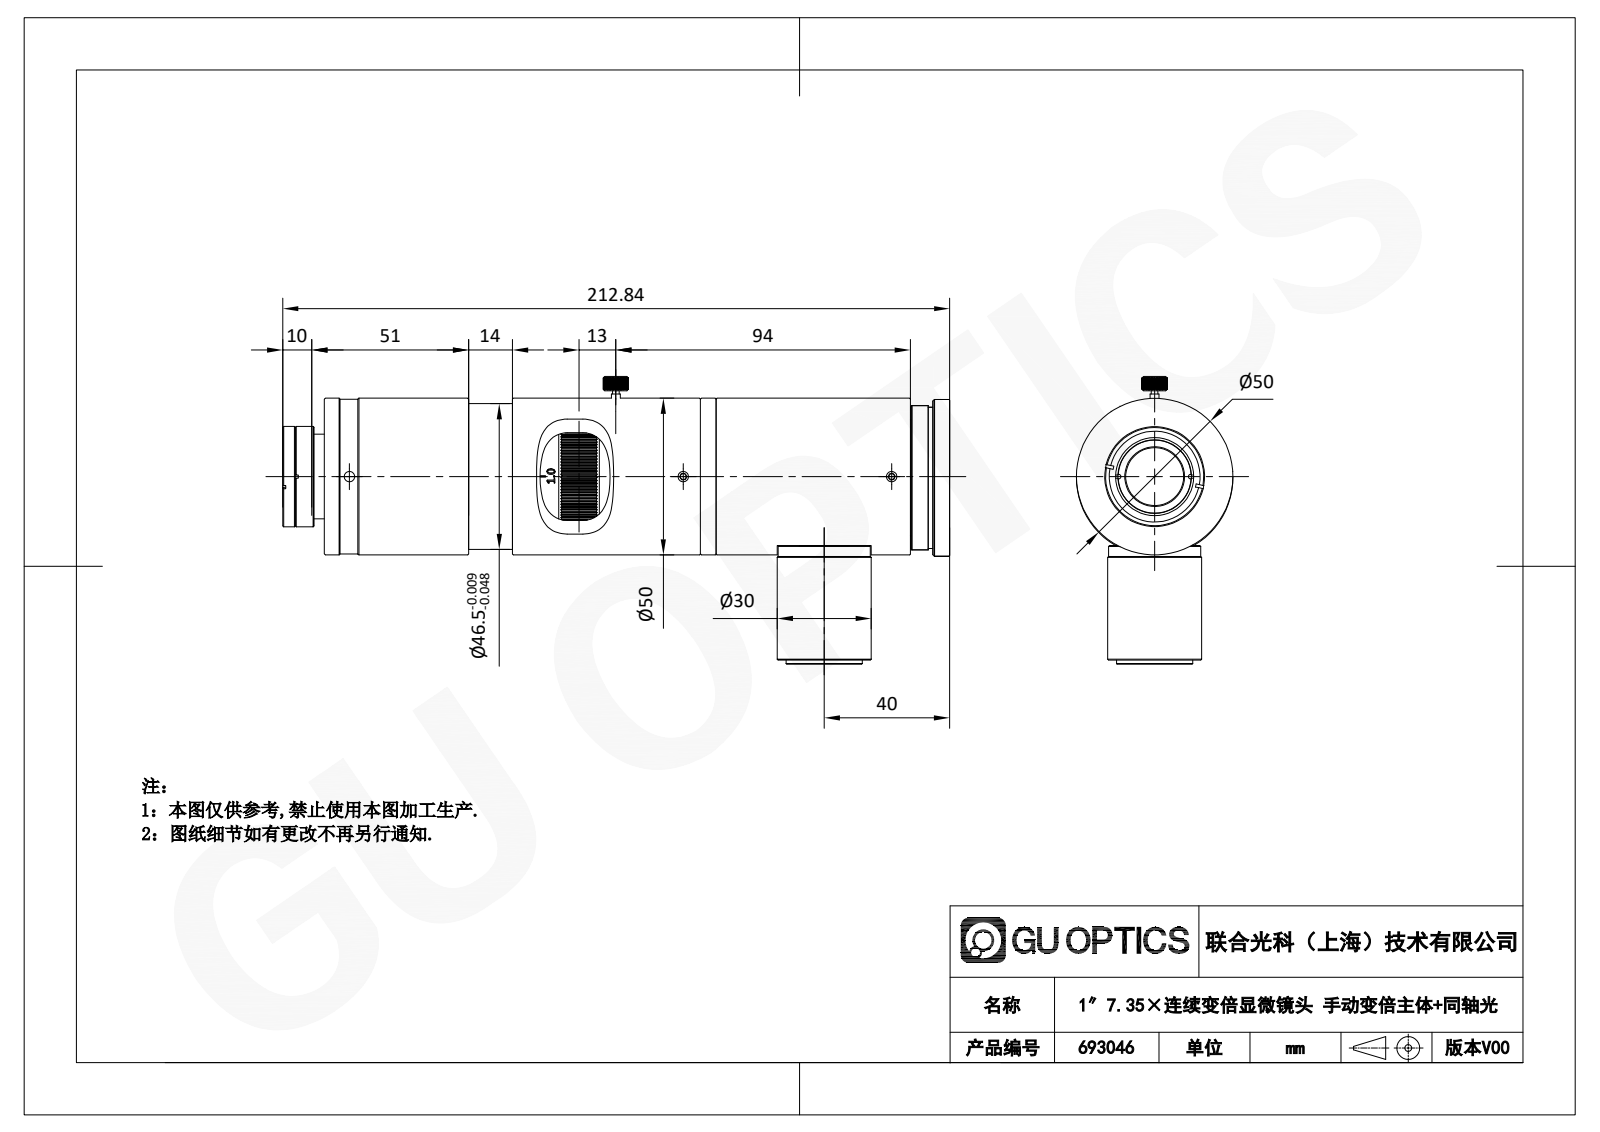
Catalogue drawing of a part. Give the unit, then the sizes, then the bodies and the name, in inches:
Units: inches
Overall size (bounding box): 8.38 × 3.612 × 1.969
Round holes (diameter × count): ⌀0.13 ×9, ⌀0.079 ×6, ⌀0.063 ×3, ⌀0.081 ×2, ⌀0.094 ×2, ⌀0.807 ×2, ⌀1.417 ×2, ⌀0.069 ×1, ⌀0.089 ×1, ⌀0.177 ×1, ⌀0.591 ×1, ⌀0.605 ×1
Round bosses / shafts (diameter × count): ⌀0.157 ×7, ⌀1.969 ×2, ⌀1.945 ×1, ⌀1.831 ×1, ⌀1.811 ×1, ⌀1.776 ×1, ⌀1.693 ×1, ⌀1.654 ×1
Partial cylindrical surfaces — rounded edges, fillets, slot ends (radius × count): R0.024 ×9, R0.03 ×6, R0.394 ×4, R0.157 ×1, R0.396 ×1, R0.807 ×1, R0.984 ×1
Main face-to-face distances: 0.079, 0.197, 5.465, 0.328, 4.843, 4.921, 4.646, 4.724, 1.002, 0.276
Hole centre spacings: 0.669, 1.159, 0.787, 2.618, 0.941, 1.033, 1.364, 1.407
Volume: 10.42 in³ · Surface area: 197.8 in²
Bodies: 22 solids, 1508 faces (739 planar, 387 cylindrical, 382 other)
Part name (STEP PRODUCT): 693046
STEP written by: SolidWorks 2020 (CONFIG_CONTROL_DESIGN)
